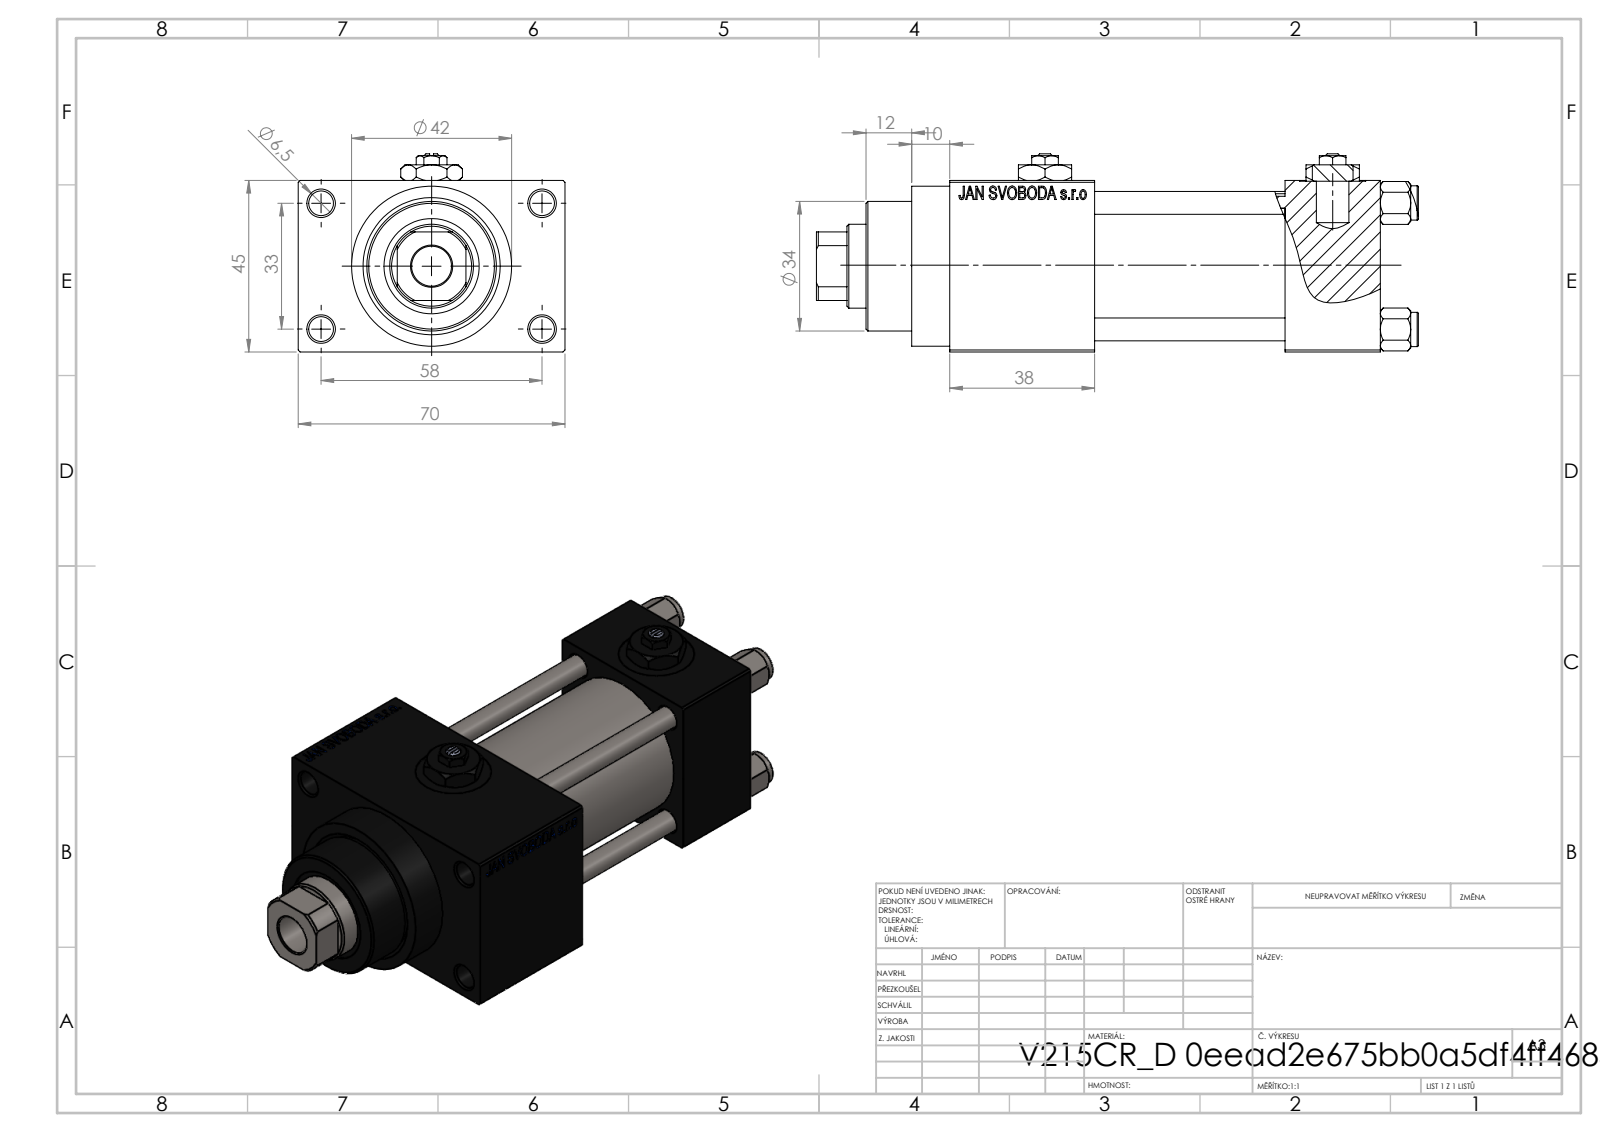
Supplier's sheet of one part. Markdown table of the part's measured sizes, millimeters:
| quantity | value |
| --- | --- |
| part name | V215CR_VCP_D; V215_VC_A; V215CR_D_Body; Zatka_pro_OIL_PORT (+2 more) |
| STEP written by | SolidWorks 2019 (CONFIG_CONTROL_DESIGN) |
| units | millimeters |
| bodies | 13 solids, 1203 faces (542 planar, 99 cylindrical, 562 other) |
| overall size | 158 × 70 × 52 |
| volume | 241 625 mm³ |
| surface area | 81 624 mm² |
| round holes (diameter × count) | 6 × 4, 6.5 × 4, 13.16 × 4, 20 × 4, 7 × 3, 10.5 × 1, 22 × 1, 24 × 1, 25 × 1, 32 × 1, 33 × 1 |
| round bosses / shafts (diameter × count) | 9 × 4, 42 × 1, 38 × 1, 34 × 1 |
| partial cylindrical surfaces (radius × count) | 10.5 × 1 |
| main face-to-face distances | 45, 25, 50, 12.5, 75, 57.5, 88, 38, 113, 70 |
| hole center spacings | 12.4, 23.48, 33.2, 33.37, 35.35, 45.6, 56.35, 33 |
